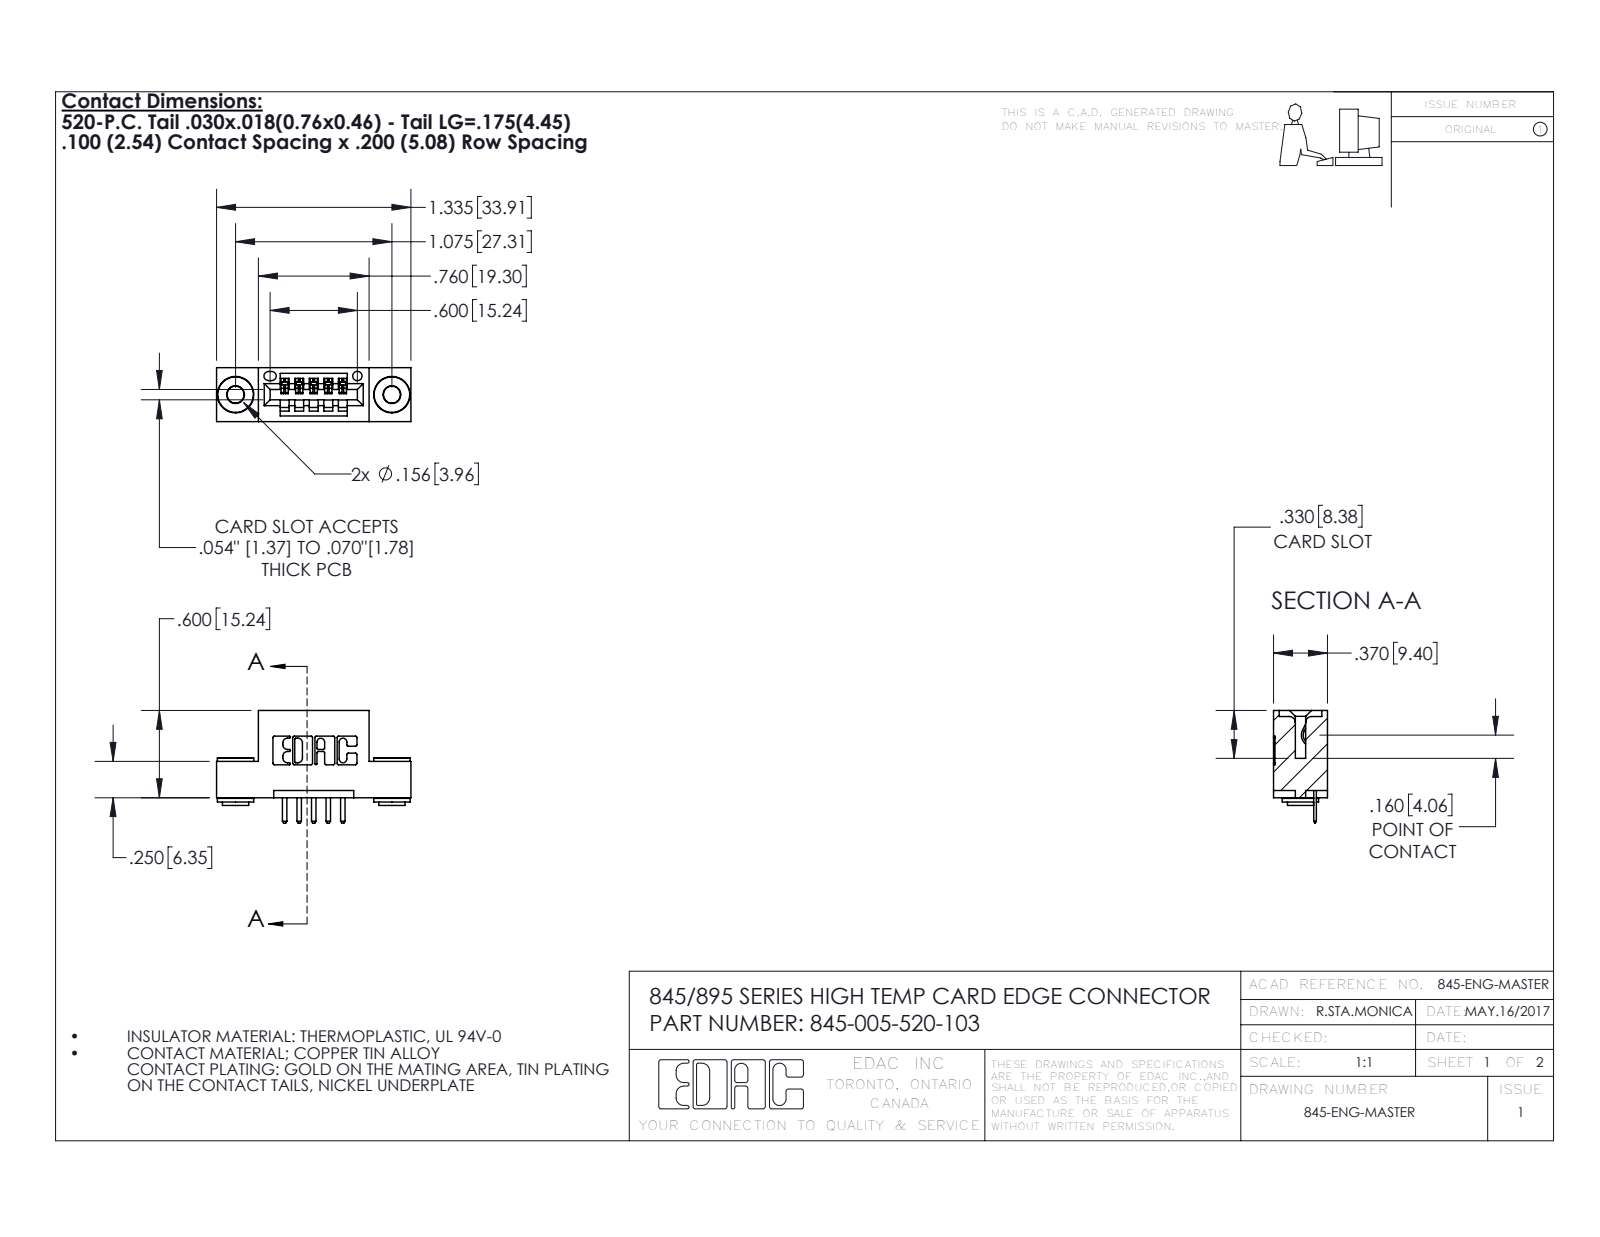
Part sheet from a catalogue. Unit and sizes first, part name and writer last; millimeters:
Units: millimetres
Overall size (bounding box): 33.9 × 19.7 × 9.4
Round holes (diameter × count): ⌀2.9 ×2, ⌀4 ×2, ⌀1.6 ×1
Round bosses / shafts (diameter × count): ⌀6.4 ×2, ⌀4.6 ×2, ⌀3.5 ×2
Partial cylindrical surfaces — rounded edges, fillets, slot ends (radius × count): R0.3 ×22, R0.3 ×12, R0.2 ×10, R0.2 ×6, R0.8 ×6, R0.7 ×3, R0.8 ×2, R1 ×2
Main face-to-face distances: 5.1, 9.4, 2.5, 1.8, 7.6, 6.4, 0.6, 8.9, 1.5, 7.6
Hole centre spacings: 6.9, 21.5, 27.3
Volume: 2 920 mm³ · Surface area: 3 548 mm²
Bodies: 8 solids, 474 faces (300 planar, 166 cylindrical, 8 other)
Part name (STEP PRODUCT): 345-005-520-103; 345-292-001_345-293-120; 345-250-002_345-250-002-102; 345 Part_Flush Mounting Lugs - 0.156 Dia-TH
STEP written by: SolidWorks 2016 (CONFIG_CONTROL_DESIGN)
